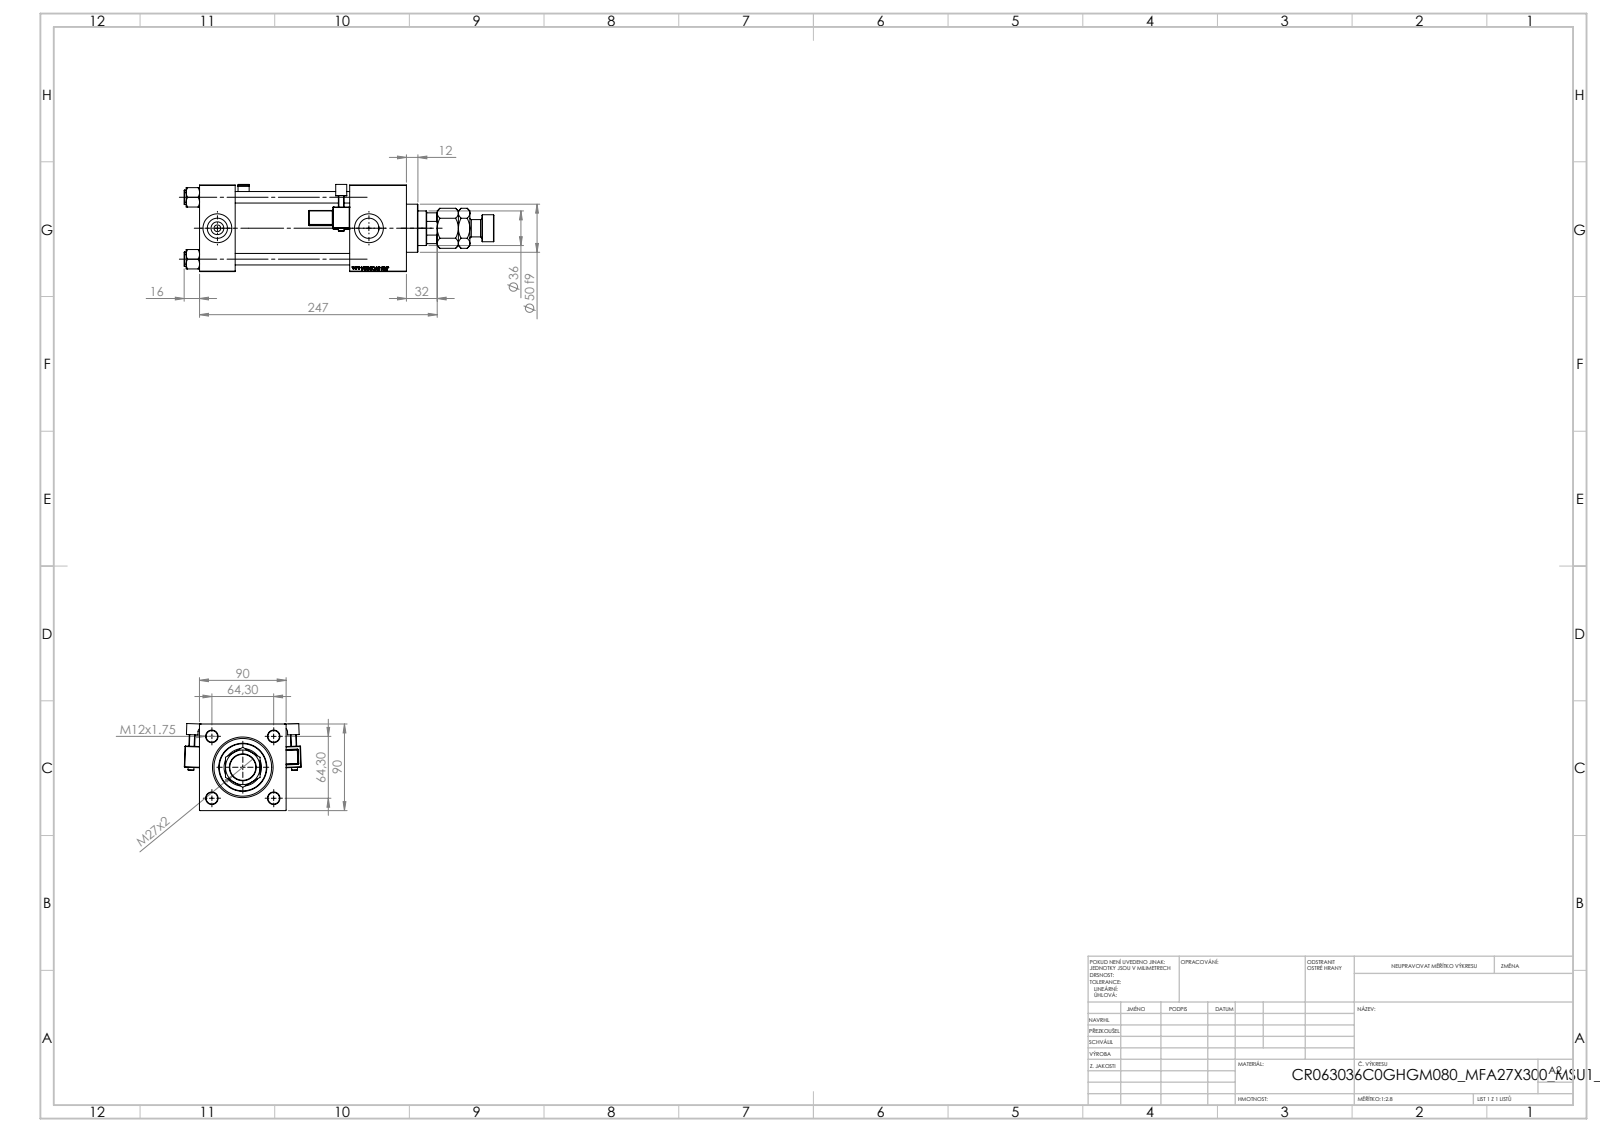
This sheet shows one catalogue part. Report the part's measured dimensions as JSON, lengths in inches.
{"part_name": "V215CR_VCP_C; V215CR_MSU; V215CR_C_TYCINKA; V215_VC_A (+3 more)", "step_written_by": "SolidWorks 2019 (CONFIG_CONTROL_DESIGN)", "units": "inches", "bodies": {"solids": 14, "faces": 1354, "planar": 600, "cylindrical": 150, "other": 604}, "overall_size": [12.677, 4.786, 3.564], "volume_in3": 72.19, "surface_area_in2": 381.3, "round_holes": [[0.472, 4], [0.276, 2], [0.825, 2], [1.181, 2], [1.004, 1], [1.417, 1], [1.535, 1], [1.969, 1], [2.362, 1], [2.48, 1]], "round_bosses_or_shafts": [[0.591, 4], [0.236, 2], [2.717, 1], [1.102, 1], [0.709, 1]], "partial_cylinders_radius": [[0.02, 48], [0.039, 2], [0.098, 2], [0.157, 2], [0.689, 1]], "face_to_face_distances": [3.543, 1.457, 2.323, 6.142, 4.685, 8.465, 7.008, 7.335, 5.878, 1.193], "hole_center_spacings": [1.79, 2.531, 3.58, 6.201]}
